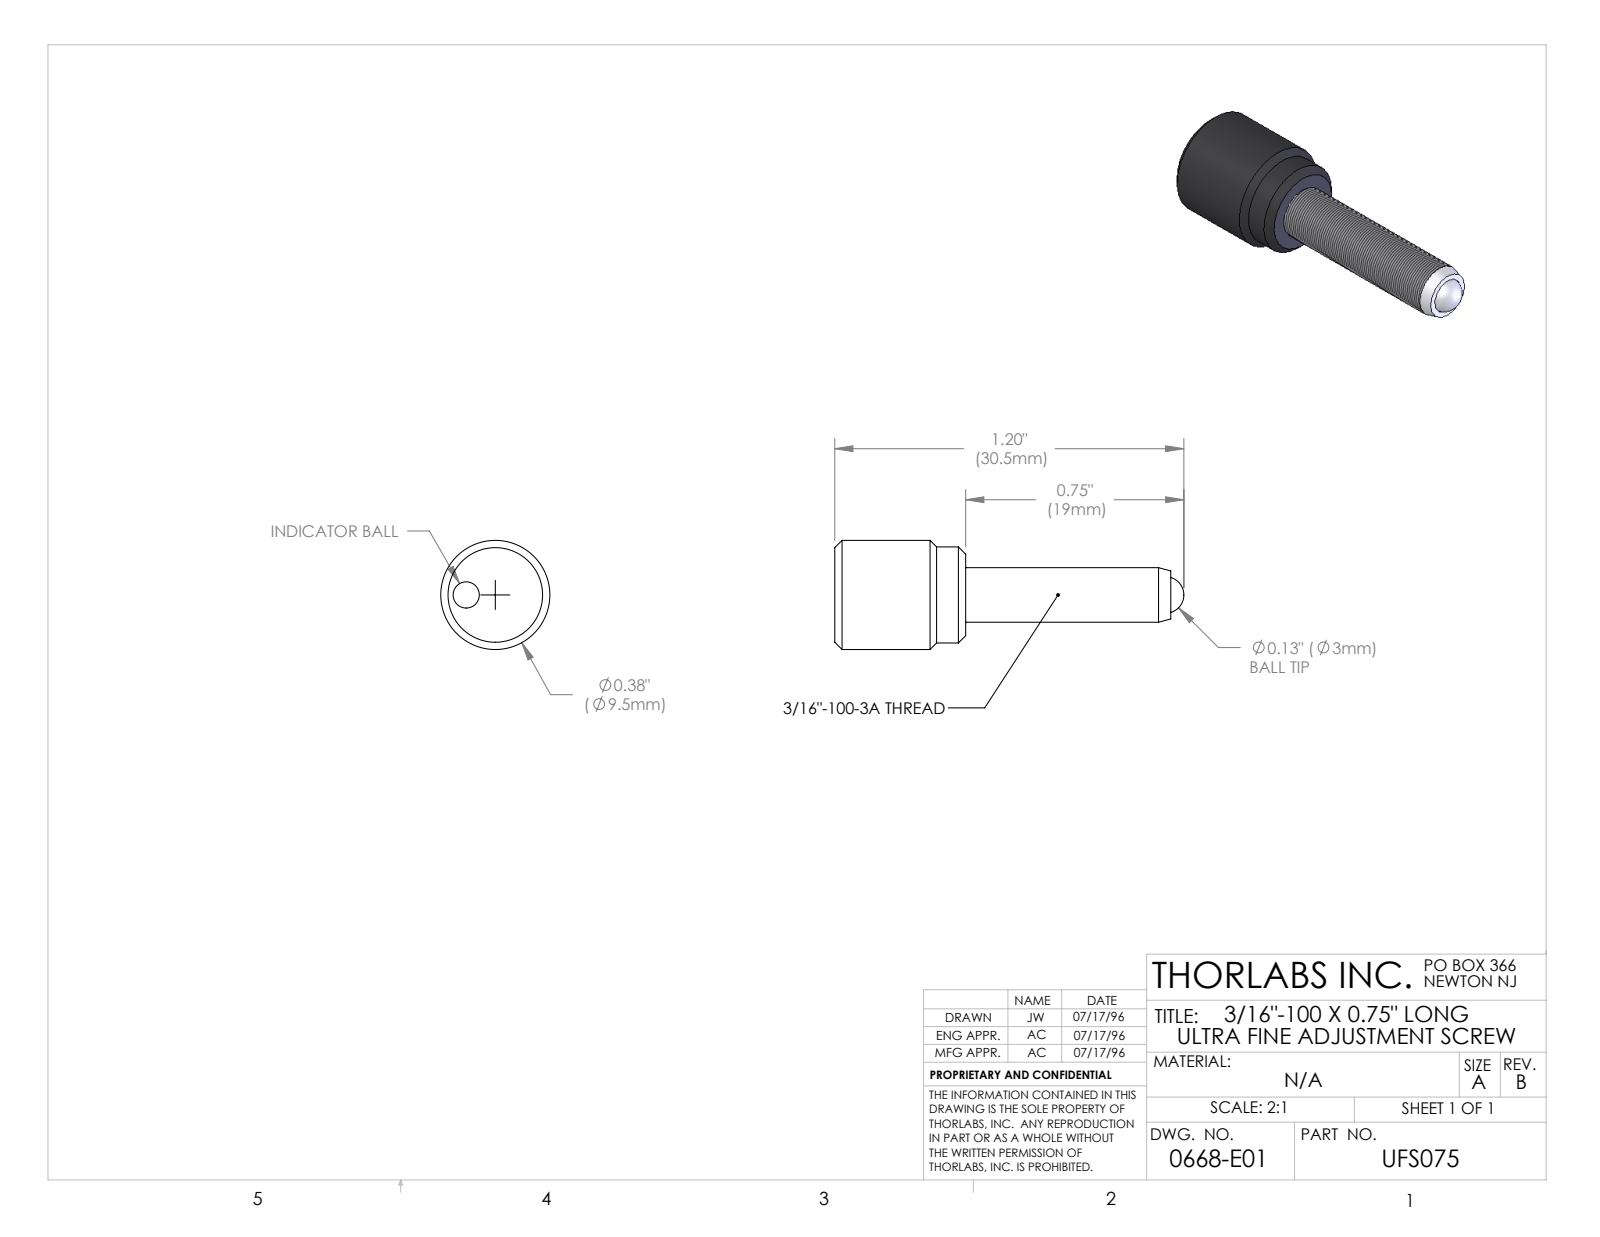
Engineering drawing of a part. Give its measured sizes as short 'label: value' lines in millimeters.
name: 0668-E0W
written by: SolidWorks 2007 (AUTOMOTIVE_DESIGN)
unit: mm
bodies: 4 solids, 39 faces (7 planar, 14 cylindrical, 18 other)
size: 30.48 × 9.53 × 9.53
volume: 1 084 mm³; area: 1 052 mm²
holes: 1× ⌀2.29, 1× ⌀3.19, 1× ⌀4.57, 1× ⌀4.72
bosses: 1× ⌀9.52, 1× ⌀8.38, 1× ⌀4.76
face distances: 3.56, 11.43, 7.87, 29.34, 25.78, 17.91, 2.29, 1.27, 9.14, 27.05
hole spacings: 2.54
